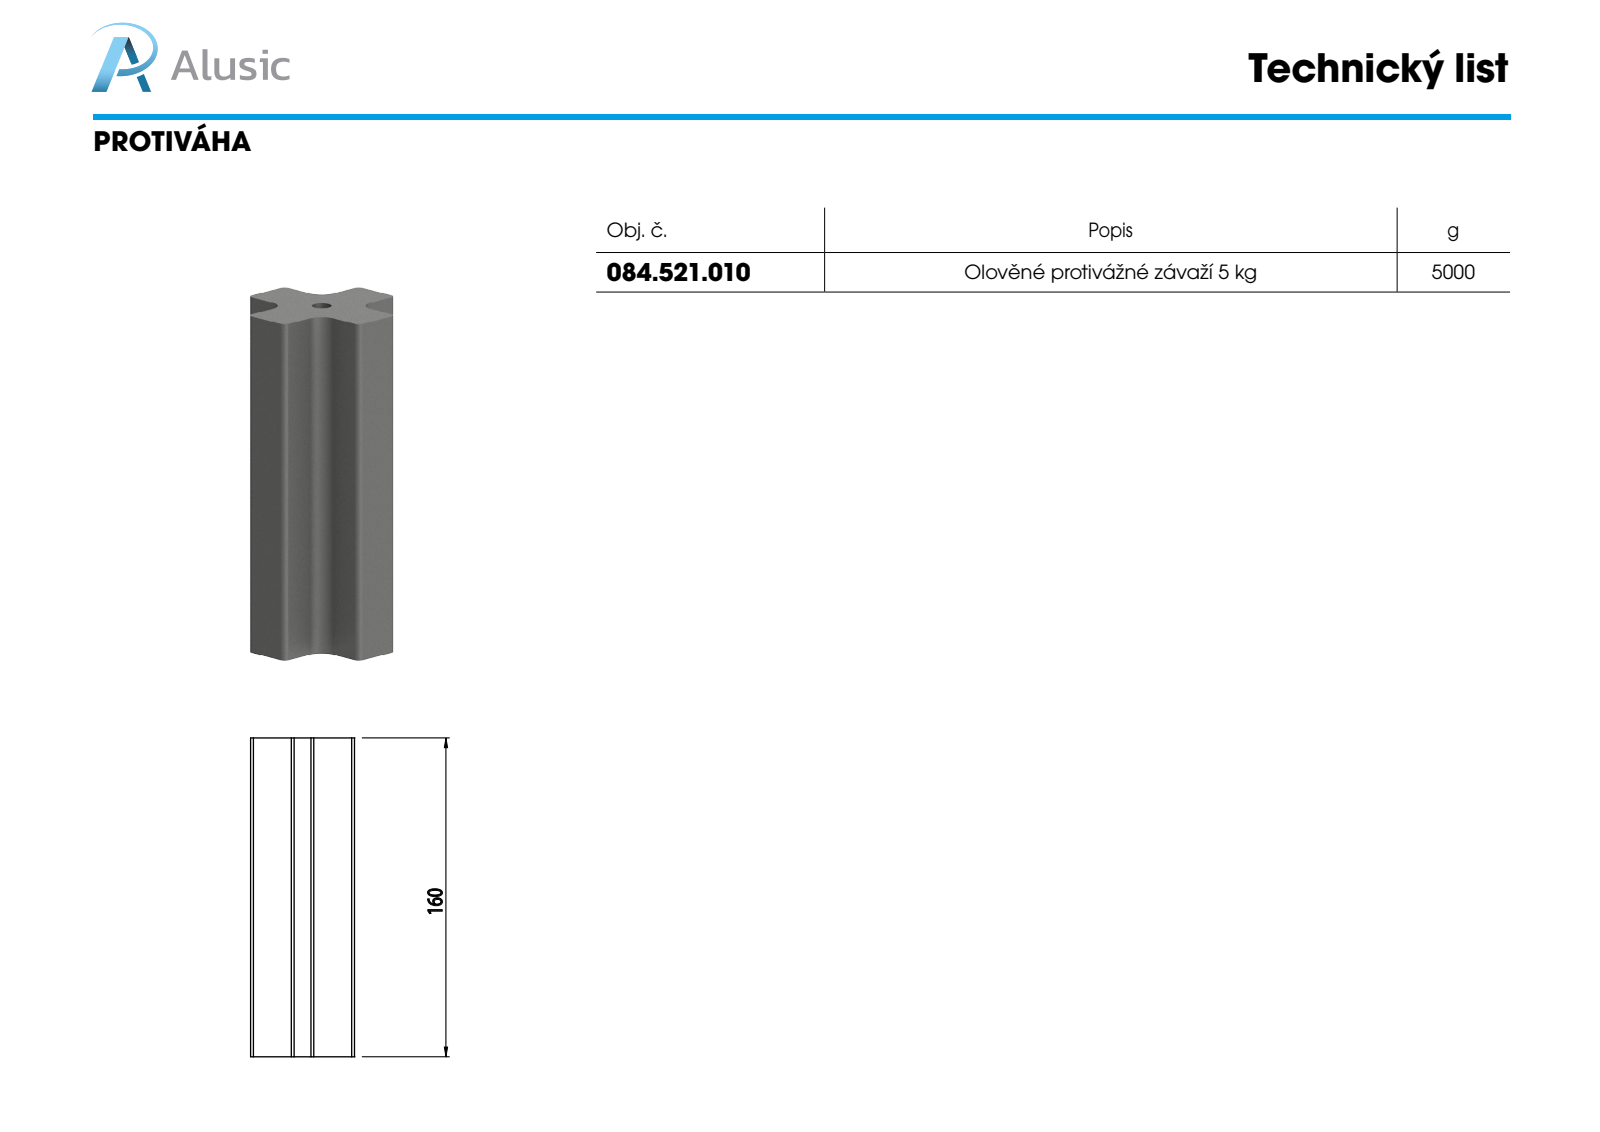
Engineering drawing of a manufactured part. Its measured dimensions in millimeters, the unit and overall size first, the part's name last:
Units: millimetres
Overall size (bounding box): 160 × 72 × 72
Round holes (diameter × count): ⌀9 ×1
Partial cylindrical surfaces — rounded edges, fillets, slot ends (radius × count): R2.7 ×8, R7.5 ×4
Main face-to-face distances: 24, 48, 72, 160
Volume: 456 344 mm³ · Surface area: 52 765 mm²
Bodies: 1 solid, 28 faces (14 planar, 14 cylindrical, 0 other)
Part name (STEP PRODUCT): 084.521.010
STEP written by: SolidWorks 2012 (CONFIG_CONTROL_DESIGN)
